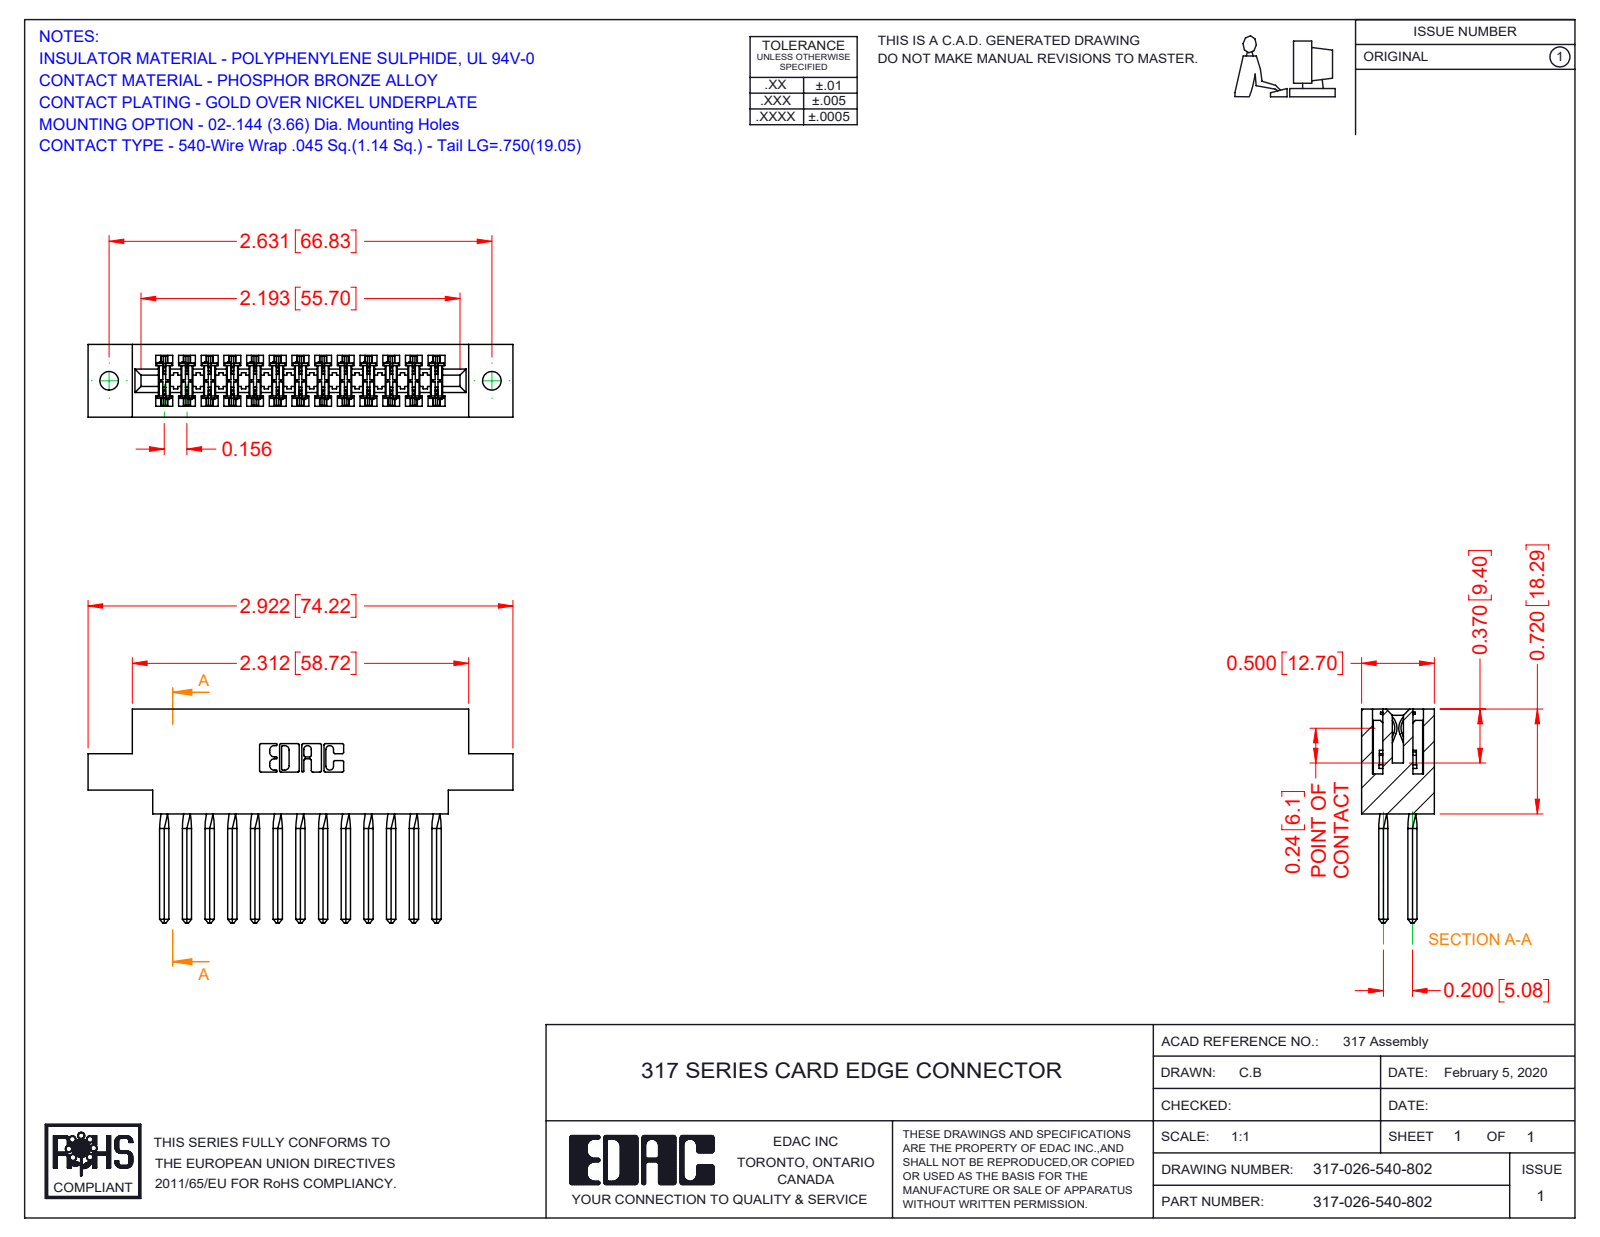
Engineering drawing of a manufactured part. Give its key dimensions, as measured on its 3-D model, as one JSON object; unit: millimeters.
{"part_name": "317-026-540-802; 317 Part_.144 Dia; 317-290-001_540", "step_written_by": "SolidWorks 2016 (CONFIG_CONTROL_DESIGN)", "units": "millimeters", "bodies": {"solids": 27, "faces": 2416, "planar": 1956, "cylindrical": 356, "other": 104}, "overall_size": [74.2, 37.3, 12.7], "volume_mm3": 11400, "surface_area_mm2": 15700, "round_holes": [[3.3, 2]], "partial_cylinders_radius": [[0.4, 52], [0.3, 22], [0.2, 6], [0.8, 6], [0.7, 3], [2.4, 2], [2.5, 2], [2.8, 2]], "face_to_face_distances": [12.7, 1.9, 10.8, 2.8, 8.9, 5.6, 8.4, 18.3, 7.7, 5], "hole_center_spacings": [66.8]}
